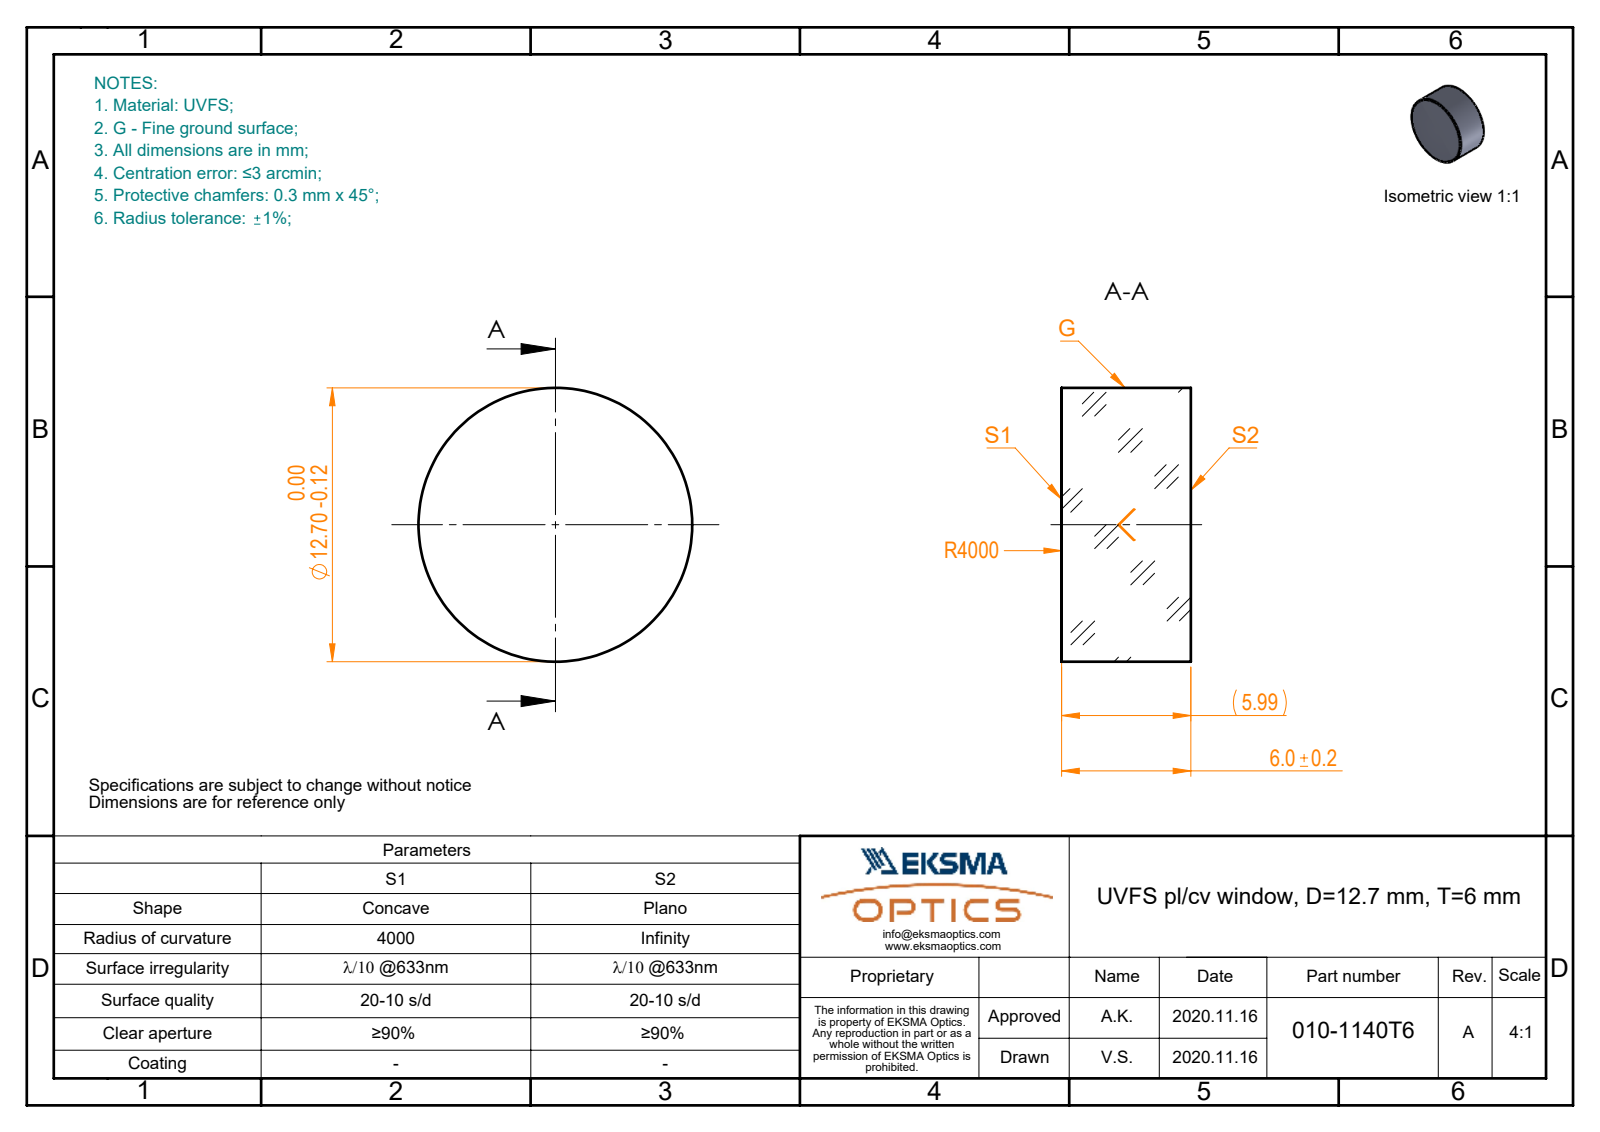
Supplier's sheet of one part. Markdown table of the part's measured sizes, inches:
| quantity | value |
| --- | --- |
| part name | 010-1140T6_UVFS_PCV_window |
| STEP written by | SolidWorks 2019 (CONFIG_CONTROL_DESIGN) |
| units | inches |
| bodies | 1 solid, 5 faces (1 planar, 2 cylindrical, 2 other) |
| overall size | 0.5 × 0.5 × 0.236 |
| volume | 0.046 in³ |
| surface area | 0.764 in² |
| round bosses / shafts (diameter × count) | 0.5 × 1 |
